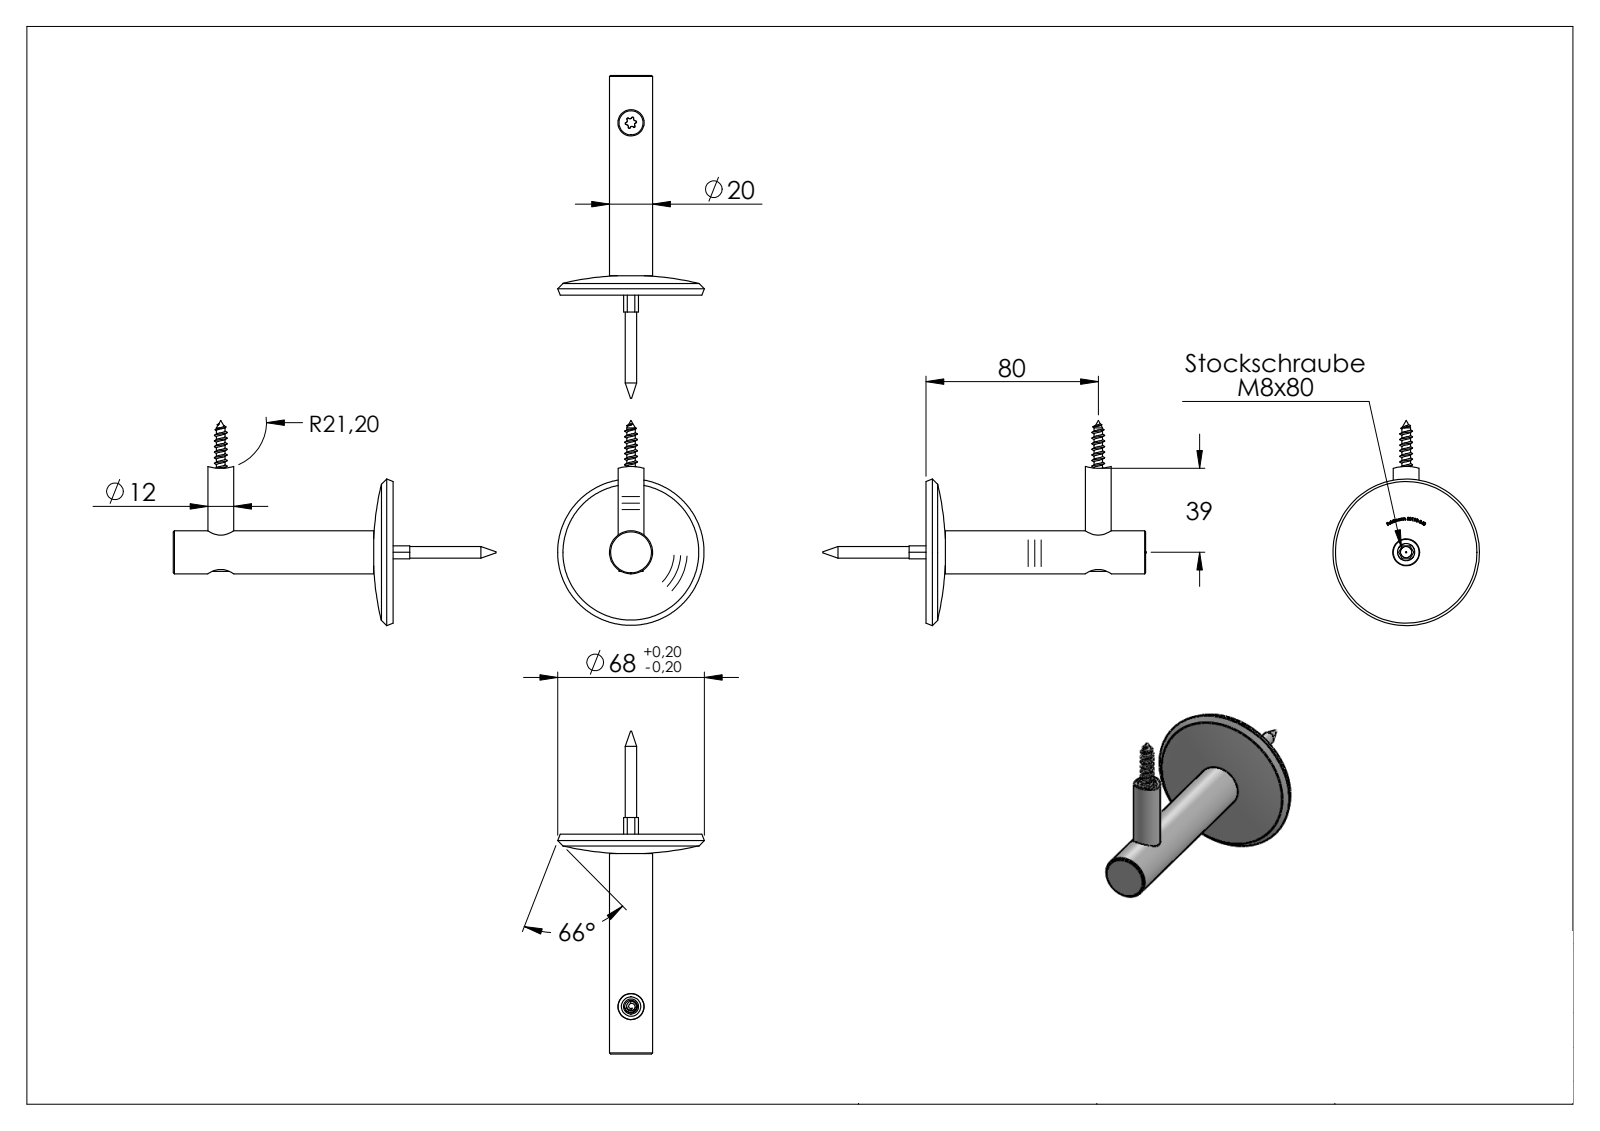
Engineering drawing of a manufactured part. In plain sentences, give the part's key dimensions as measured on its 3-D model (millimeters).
The part is named "50198-240 Teil2_50198-240 Teil2; 50198-240 Teil4_50198-240 Teil4; 50198-240 Teil1_50198-240 Teil1; 5834X-240-XX Konfig_58341-240-80 (+7 more)". Its 3-D file was written by "SolidWorks 2018 (CONFIG_CONTROL_DESIGN)". It is 5 solids with 635 faces: 248 planar, 93 cylindrical and 294 other. Overall it measures 149.76 by 95.21 by 68 millimeters. Its volume is 49 491 cubic millimeters and its surface area 21 540 square millimeters. Round holes: 1 of diameter 6.8, 1 of diameter 7, 1 of diameter 9, 1 of diameter 12.1, 1 of diameter 12.2, 1 of diameter 12.5. Round bosses or shafts: 2 of diameter 12, 1 of diameter 20, 1 of diameter 11.2, 1 of diameter 8, 1 of diameter 5.3, 1 of diameter 4. Partial cylindrical surfaces (rounded edges, fillets, slot ends): 6 of radius 0.48, 6 of radius 0.84, 1 of radius 21.2. The main face-to-face distances are 6, 8.79, 95, 3, 11.79, 5.79, 25.24, 69.76, 4.76, 30.
